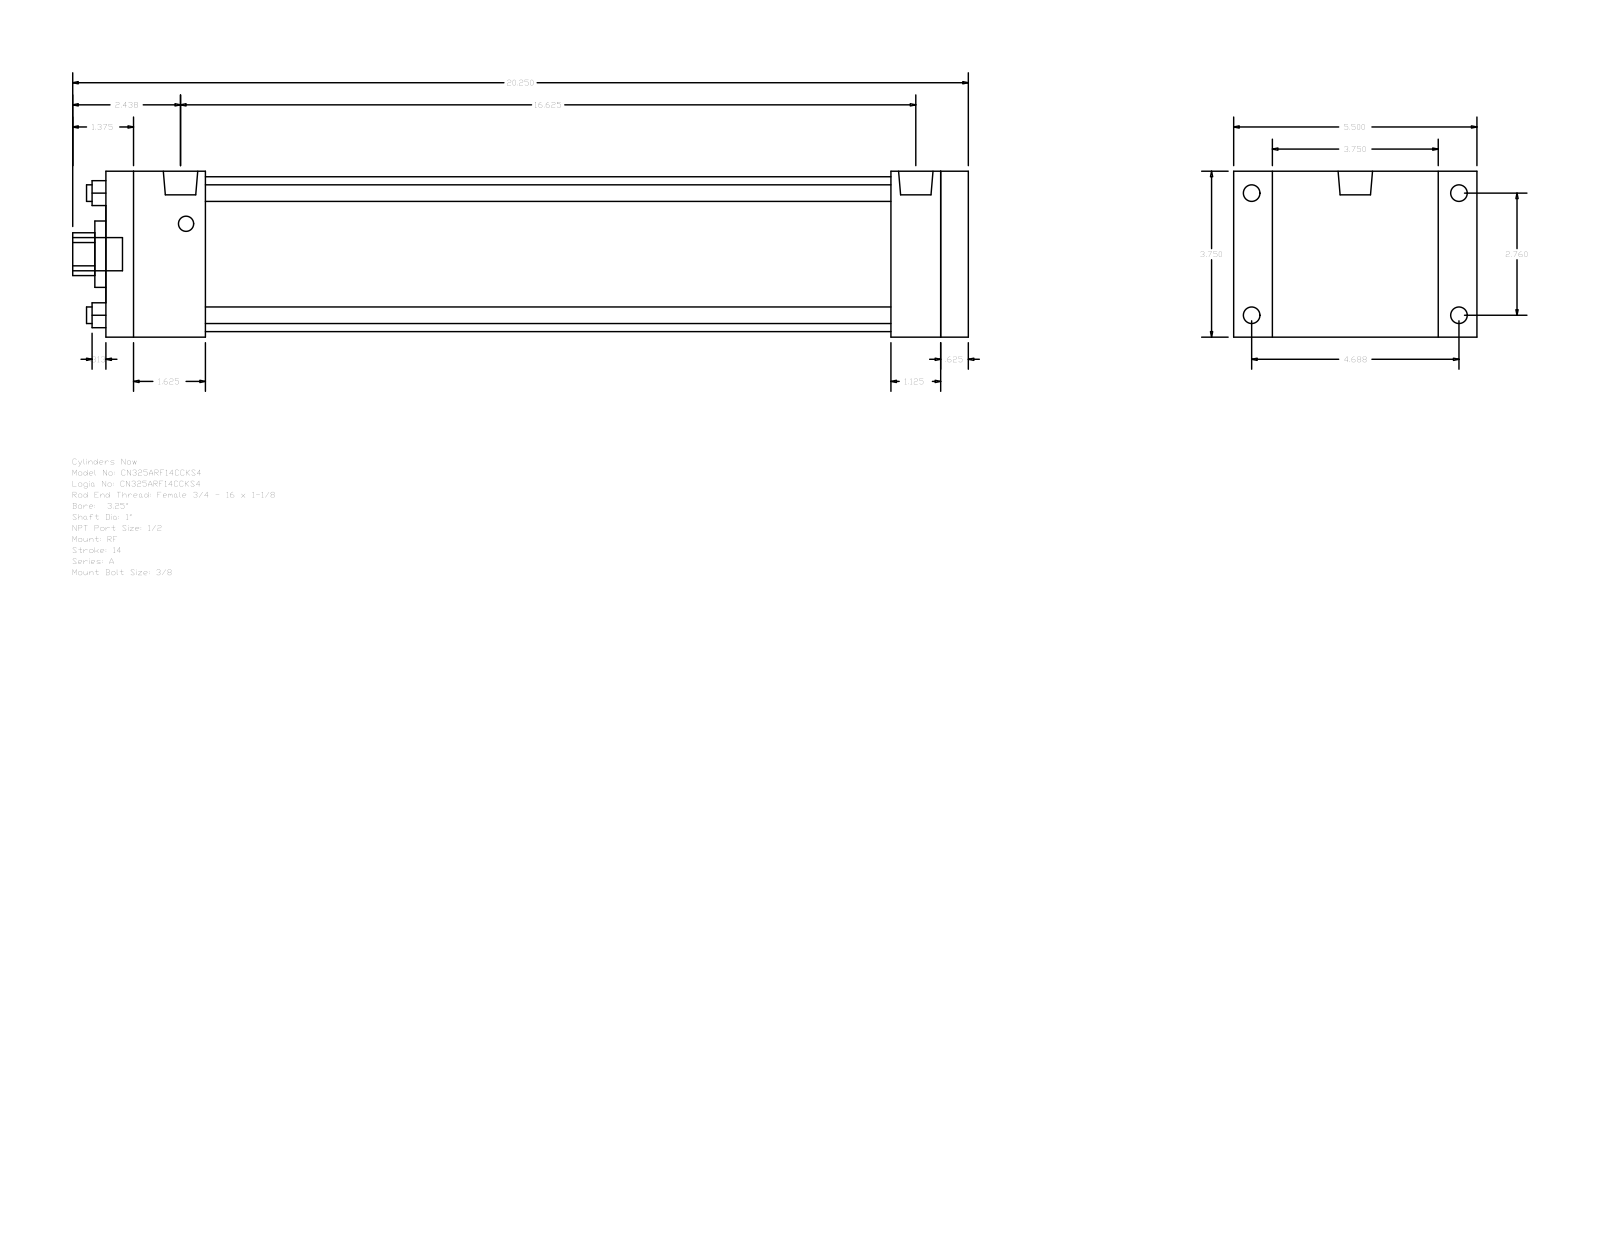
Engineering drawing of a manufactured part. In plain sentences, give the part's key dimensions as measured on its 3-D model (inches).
The part is named "A_RF__0325_1". Its 3-D file was written by "GSSL Pune (CONFIG_CONTROL_DESIGN)". It is 0 solids with 92 faces: 64 planar, 28 cylindrical and 0 other. Overall it measures 20.25 by 5.5 by 3.75 inches. Round holes: 4 of diameter 0.375, 1 of diameter 1, 1 of diameter 1.5, 1 of diameter 3.5. Round bosses or shafts: 4 of diameter 0.375, 4 of diameter 0.344, 2 of diameter 0.778, 1 of diameter 0.75. Partial cylindrical surfaces (rounded edges, fillets, slot ends): 1 of radius 0.484. The main face-to-face distances are 3.75, 19.5, 0.625, 18.875, 0.875, 4.625, 17.75, 1.125, 1.75, 2.25. The hole center spacings are 1.952, 2.76, 3.903.
